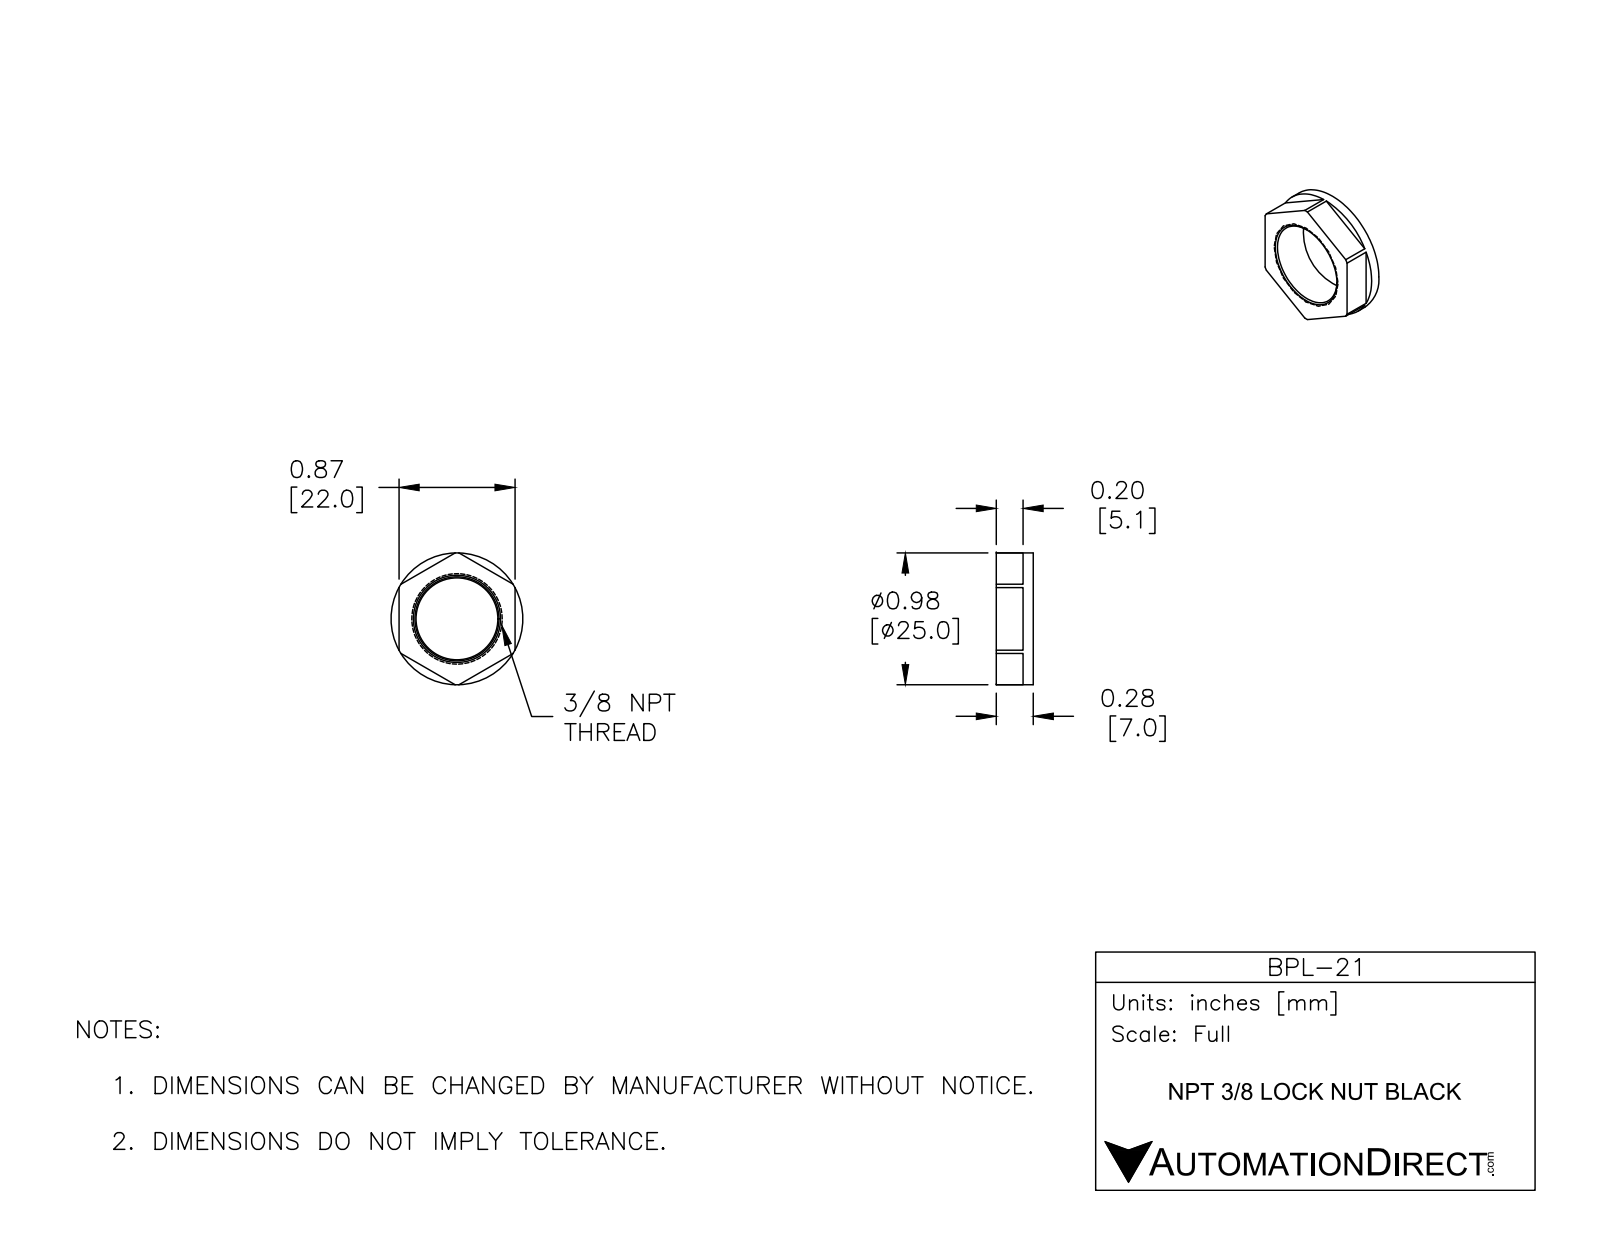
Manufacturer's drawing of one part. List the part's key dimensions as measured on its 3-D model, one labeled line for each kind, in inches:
Part name (STEP PRODUCT): BPL-21
STEP written by: SolidWorks 2015 (CONFIG_CONTROL_DESIGN)
Units: inches
Bodies: 1 solid, 20 faces (14 planar, 2 cylindrical, 4 other)
Overall size (bounding box): 0.984 × 0.984 × 0.276
Volume: 0.09 in³ · Surface area: 2.2 in²
Round bosses / shafts (diameter × count): ⌀0.984 ×1
Main face-to-face distances: 0.866, 0.276, 0.076, 0.2
